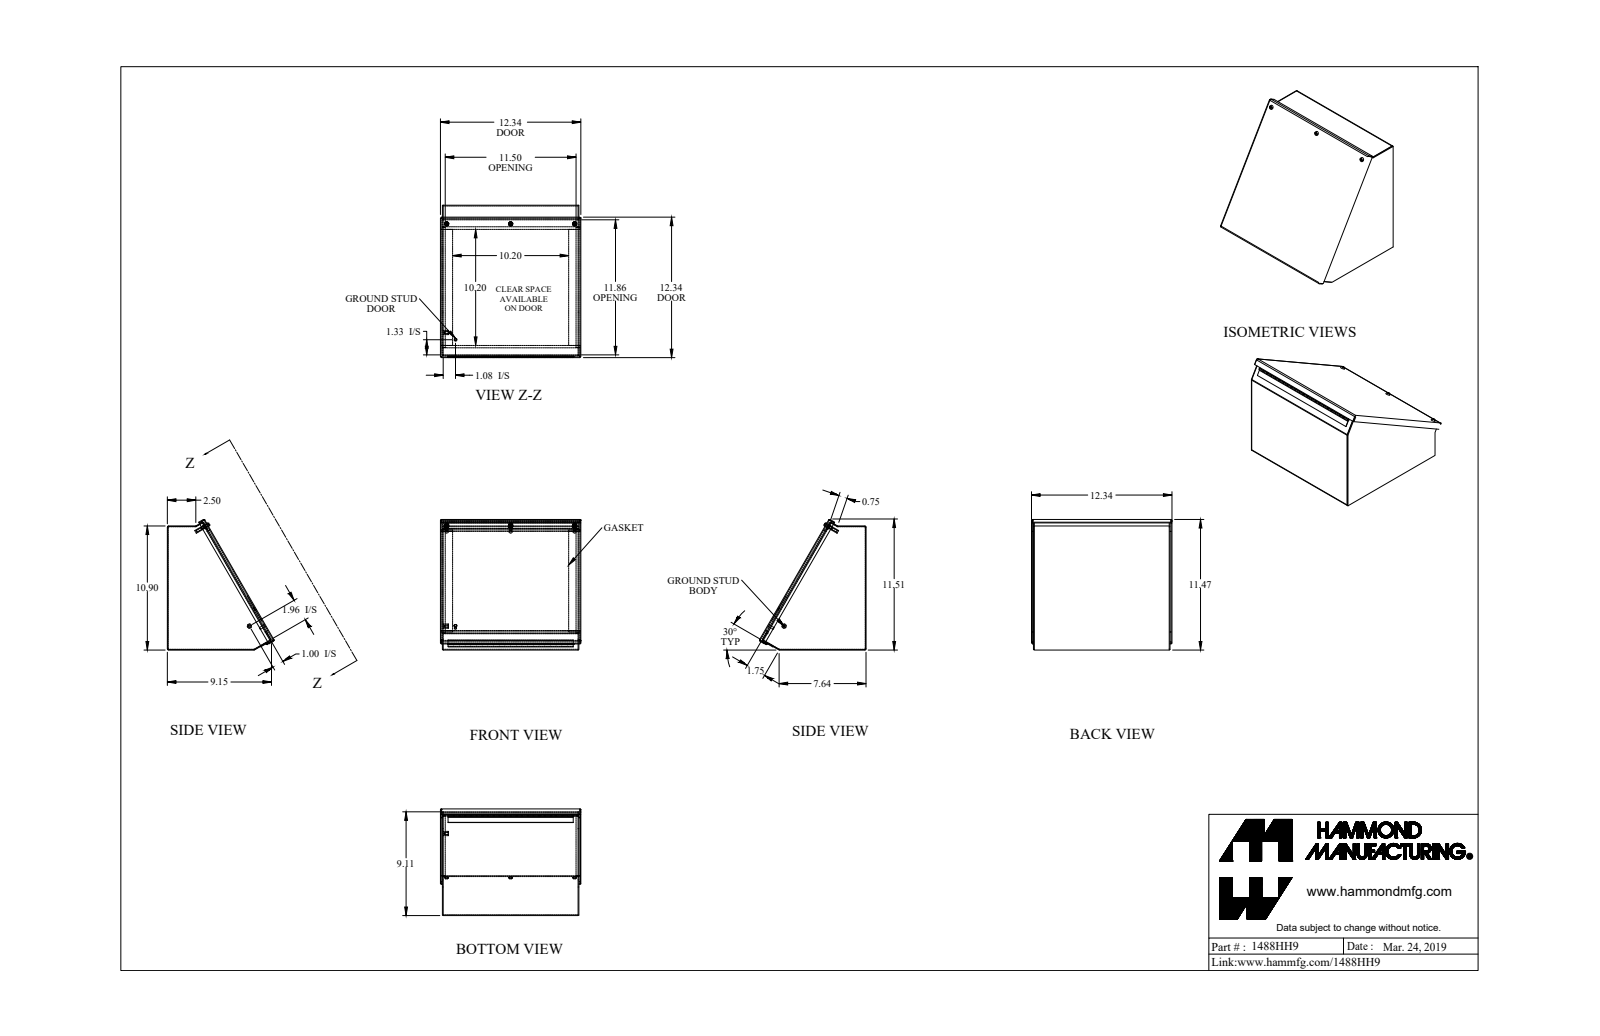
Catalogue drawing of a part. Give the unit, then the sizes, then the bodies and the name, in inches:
Units: inches
Overall size (bounding box): 12.343 × 11.472 × 9.372
Round holes (diameter × count): ⌀0.159 ×3, ⌀0.25 ×3, ⌀0.05 ×1, ⌀0.156 ×1
Round bosses / shafts (diameter × count): ⌀0.39 ×3, ⌀0.275 ×3, ⌀0.19 ×3, ⌀0.148 ×3, ⌀0.375 ×1, ⌀0.25 ×1, ⌀0.188 ×1, ⌀0.1 ×1
Partial cylindrical surfaces — rounded edges, fillets, slot ends (radius × count): R0.036 ×12, R0.108 ×12, R0.125 ×3, R0.16 ×3, R0.171 ×3, R0.055 ×1, R0.057 ×1
Main face-to-face distances: 0.072, 11.928, 11.856, 12, 10.828, 0.322, 0.25, 0.072, 0.125, 0.197
Hole centre spacings: 5.625, 5.625, 11.25, 11.25, 2.224
Volume: 55.71 in³ · Surface area: 1 386 in²
Bodies: 22 solids, 574 faces (349 planar, 189 cylindrical, 36 other)
Part name (STEP PRODUCT): 1488HH9_Default
STEP written by: SolidWorks 2019 (CONFIG_CONTROL_DESIGN)
